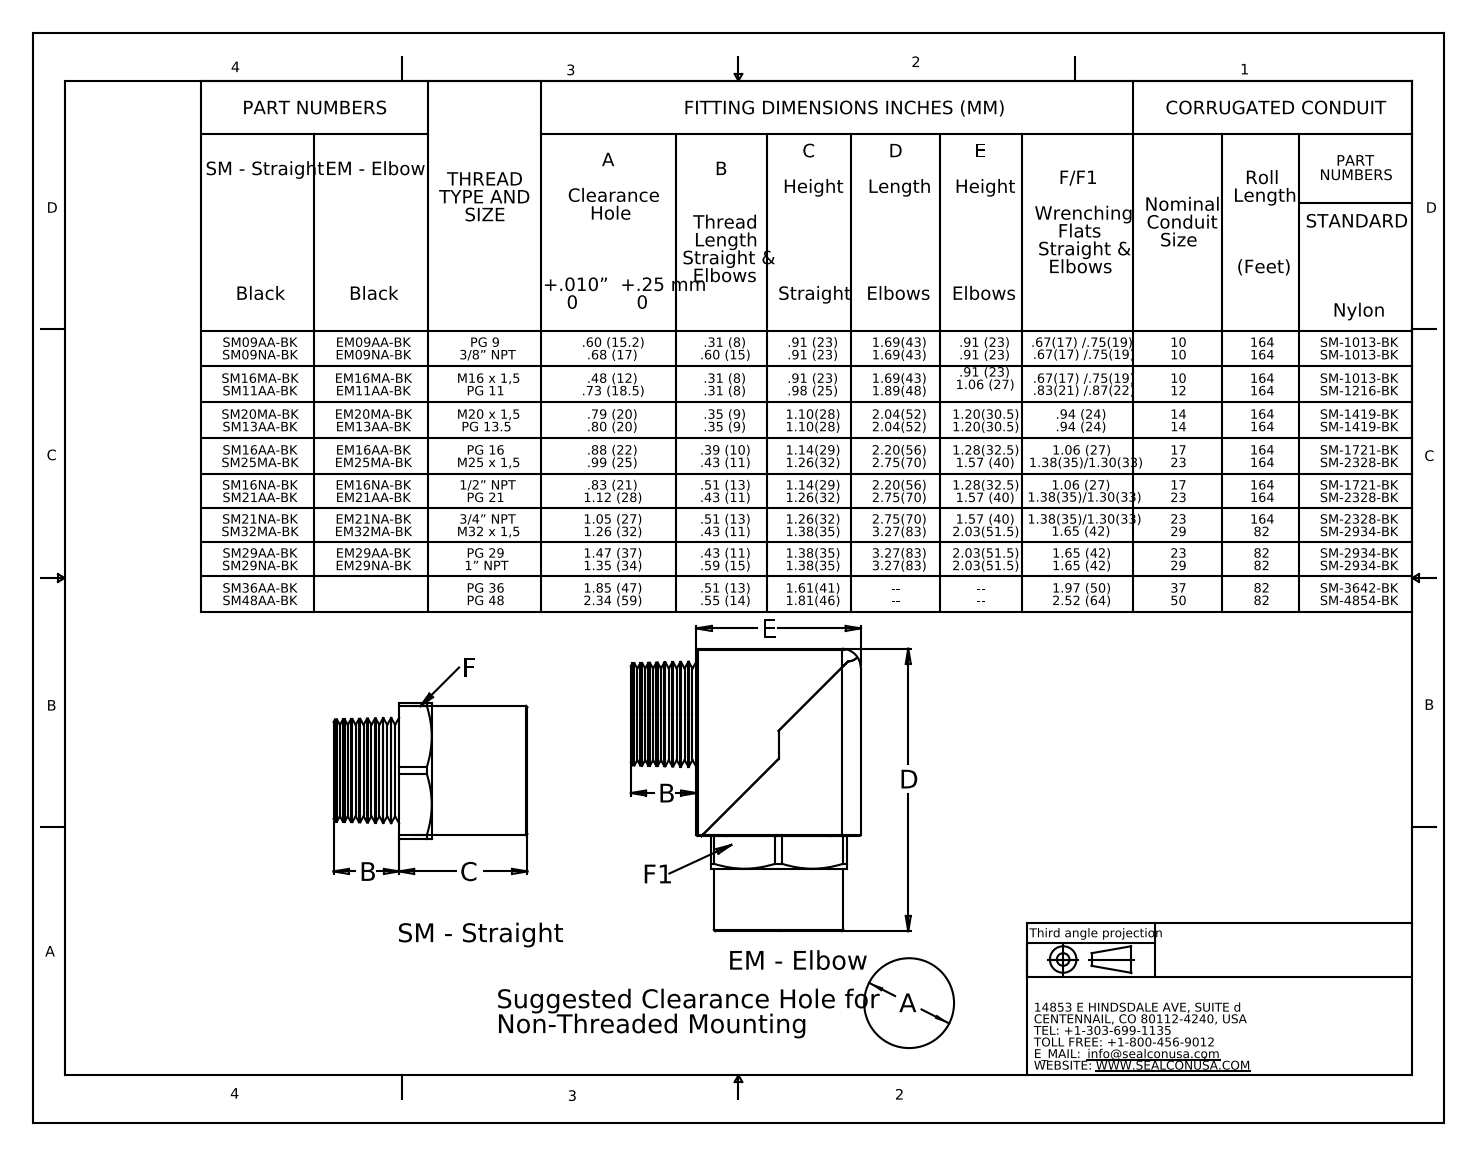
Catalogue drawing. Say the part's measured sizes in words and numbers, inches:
The part is named "SM36AA-BK". Its 3-D file was written by "SolidWorks 2009 (CONFIG_CONTROL_DESIGN)". It is 1 solid with 91 faces: 11 planar, 11 cylindrical and 69 other. Overall it measures 2.216 by 2.12 by 1.97 inches. Its volume is 2.111 cubic inches and its surface area 29.49 square inches. Round holes: 1 of diameter 1.7. Round bosses or shafts: 1 of diameter 1.871. Partial cylindrical surfaces (rounded edges, fillets, slot ends): 1 of radius 1.108. The main face-to-face distances are 0.765, 1.97, 0.255, 0.51, 1.355, 1.61, 2.12.
